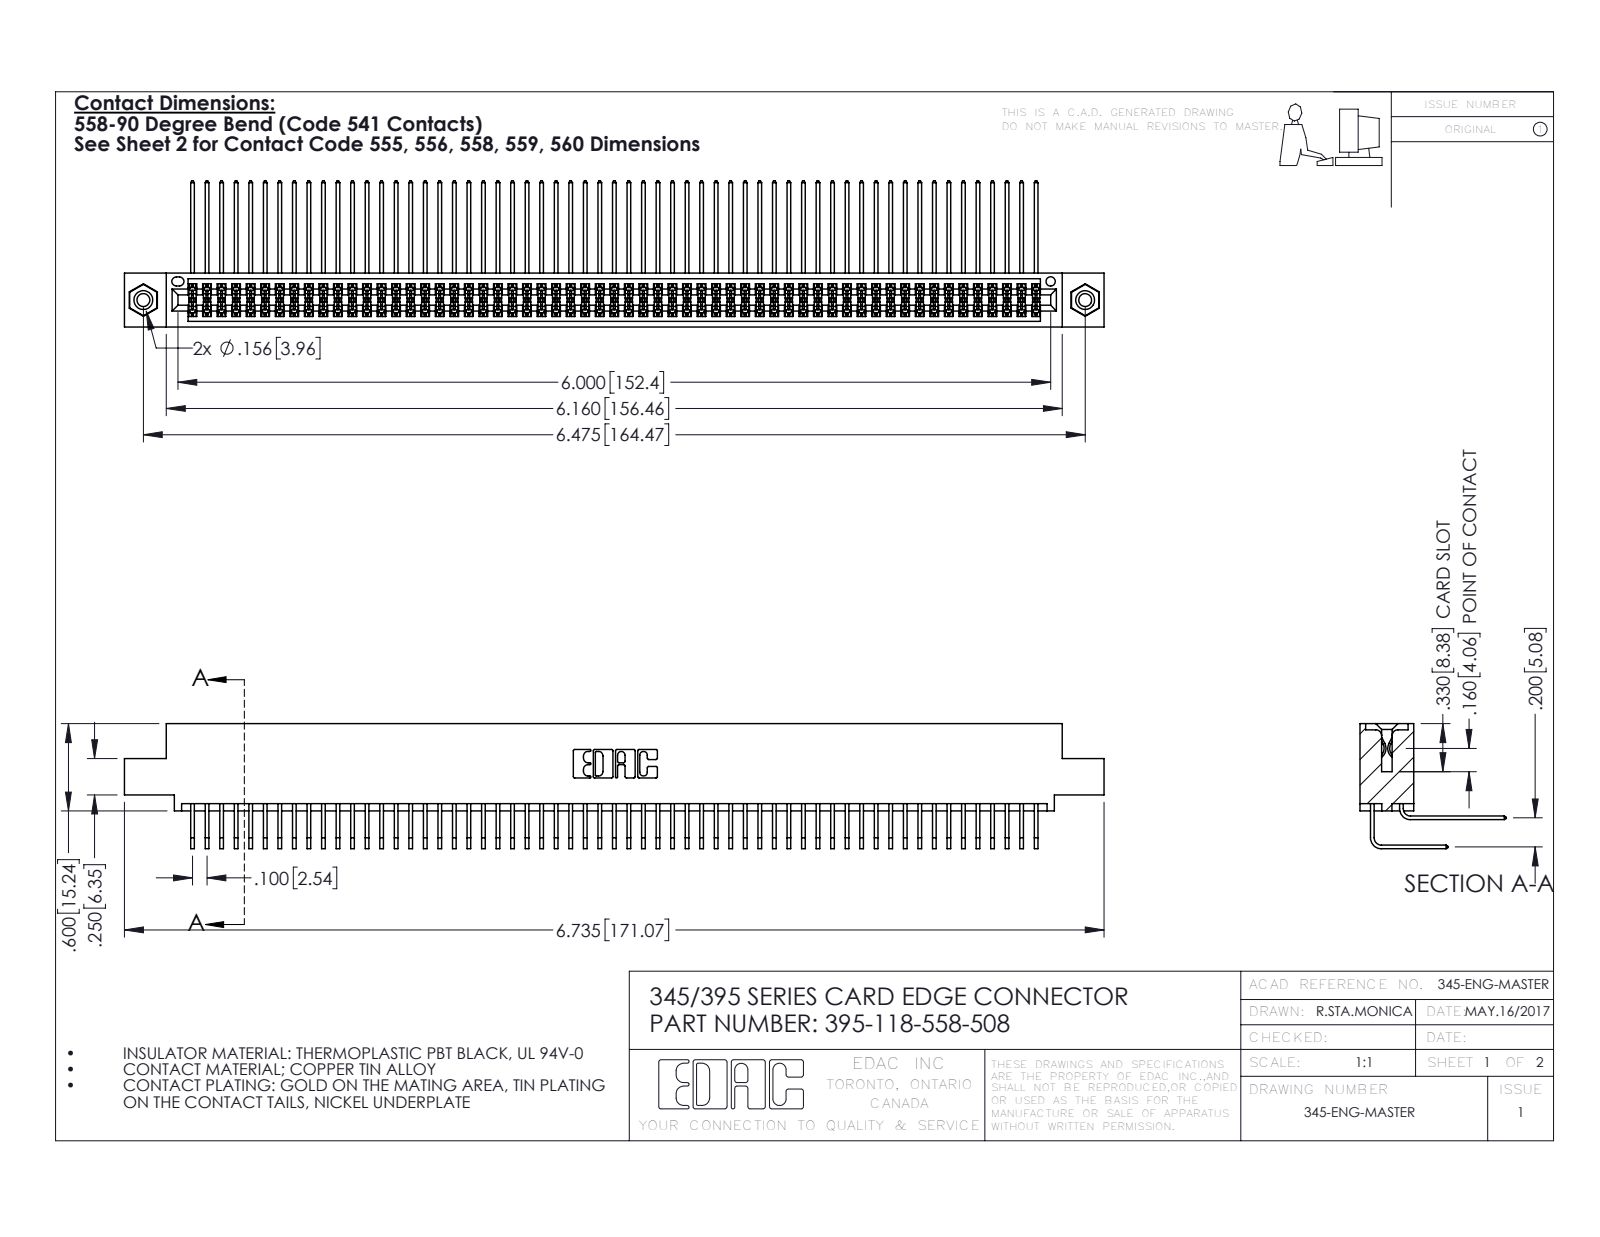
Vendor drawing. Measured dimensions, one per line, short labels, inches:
name: 345-250-001_345-250-003-102; 345 Part_0.110 Offset - 0.156 Dia-TI; 345-292-001_558 559 Tail - 1; 395-118-558-508 (+1 more)
written by: SolidWorks 2016 (CONFIG_CONTROL_DESIGN)
unit: in
bodies: 121 solids, 6326 faces (4246 planar, 2064 cylindrical, 16 other)
size: 6.735 × 1.005 × 0.859
volume: 1.06 in³; area: 45.45 in²
holes: 2× ⌀0.089, 2× ⌀0.125, 2× ⌀0.156, 1× ⌀0.064
bosses: 2× ⌀0.155
rounds: 178× R0.006, 22× R0.01, 6× R0.007, 6× R0.031, 3× R0.026, 2× R0.014, 2× R0.019, 2× R0.022
face distances: 0.072, 0.298, 0.2, 0.37, 0.098, 0.272, 0.025, 0.225, 0.025, 0.175
hole spacings: 0.27, 6.239, 6.475
